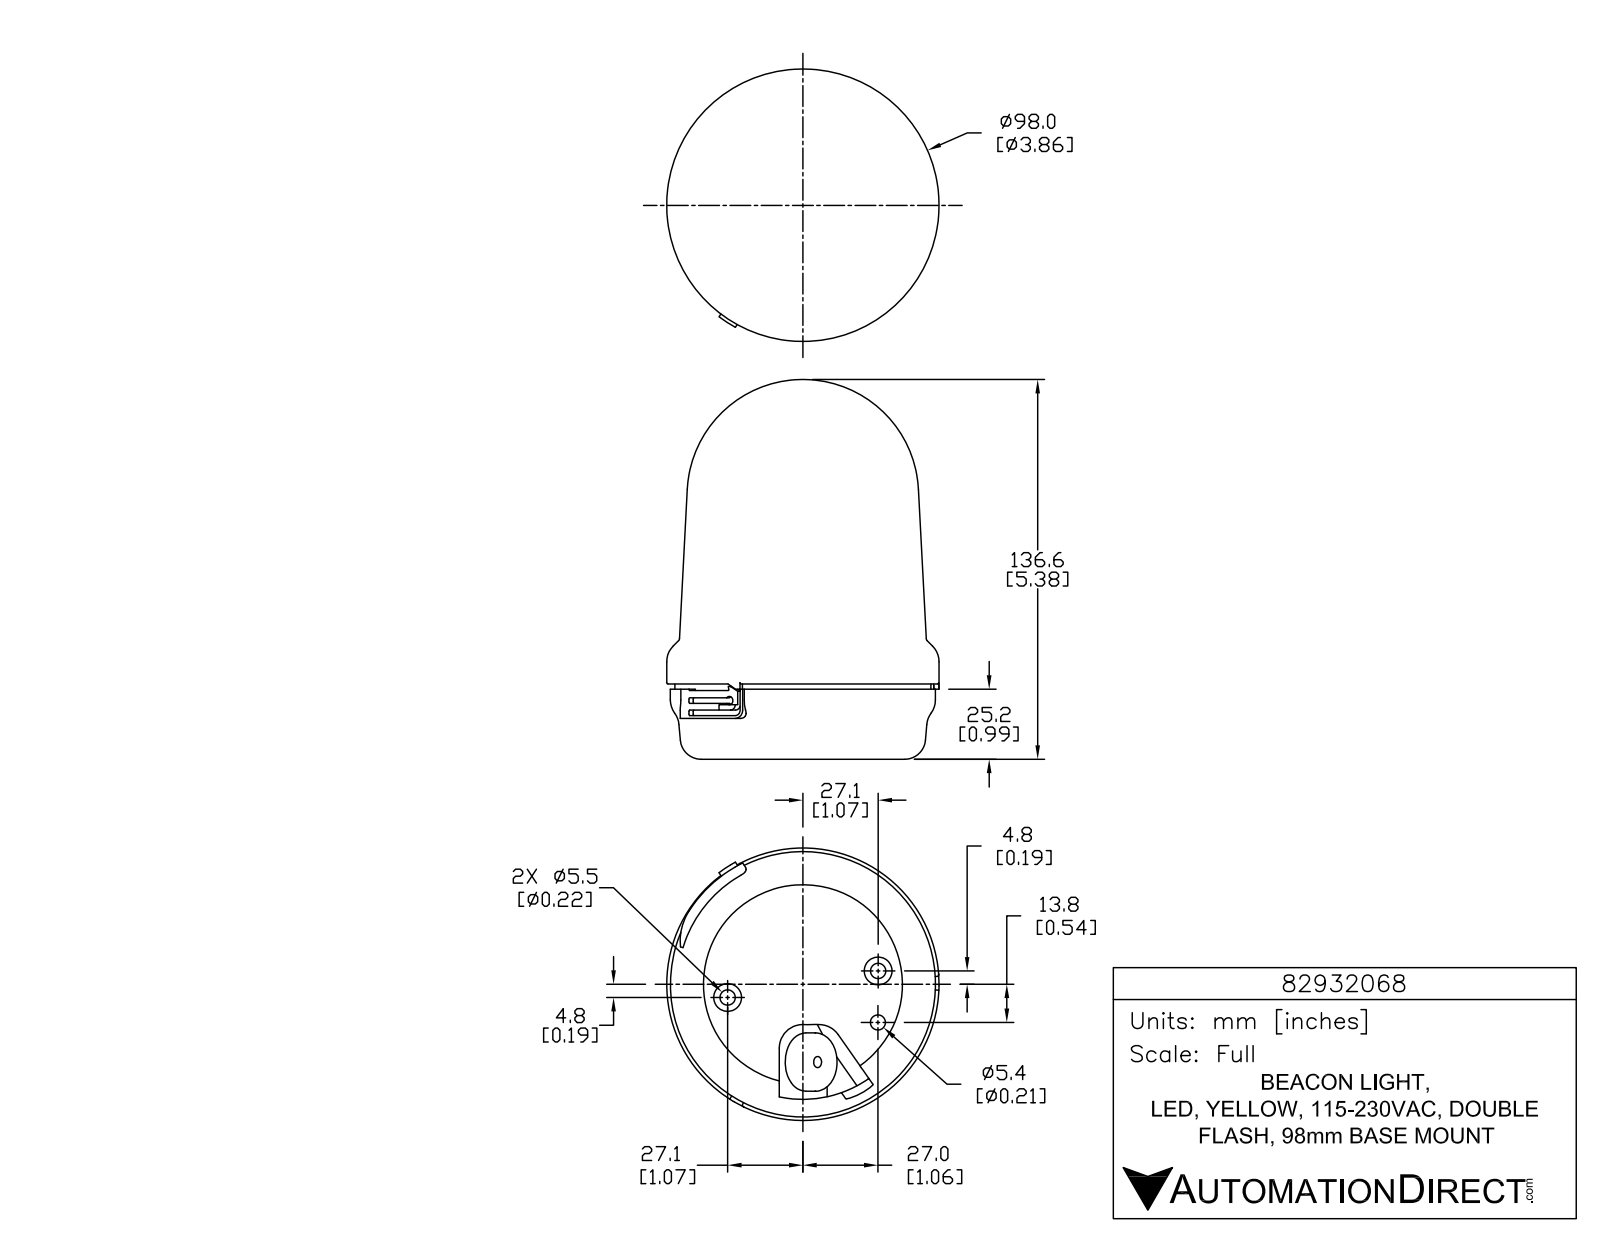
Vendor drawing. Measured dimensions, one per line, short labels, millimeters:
name: 82932068
written by: SolidWorks 2015 (AUTOMOTIVE_DESIGN)
unit: mm
bodies: 1 solid, 872 faces (566 planar, 204 cylindrical, 102 other)
size: 136.6 × 98 × 98
volume: 732 300 mm³; area: 47 520 mm²
holes: 3× ⌀1.5, 2× ⌀5.5, 1× ⌀4, 1× ⌀5.4, 1× ⌀71.6
bosses: 3× ⌀8.6, 3× ⌀2.1, 2× ⌀10, 1× ⌀98, 1× ⌀95.4, 1× ⌀92.1, 1× ⌀21
rounds: 9× R0.1, 6× R0.1, 6× R0.3, 6× R0.3, 6× R0.3, 6× R5, 5× R0.5, 4× R1
face distances: 26.5, 24.7, 1.9, 0.5, 25.2, 27.1, 6, 14.7, 14.2, 10.5
hole spacings: 27.5, 18.5, 30.3, 54.8, 55
